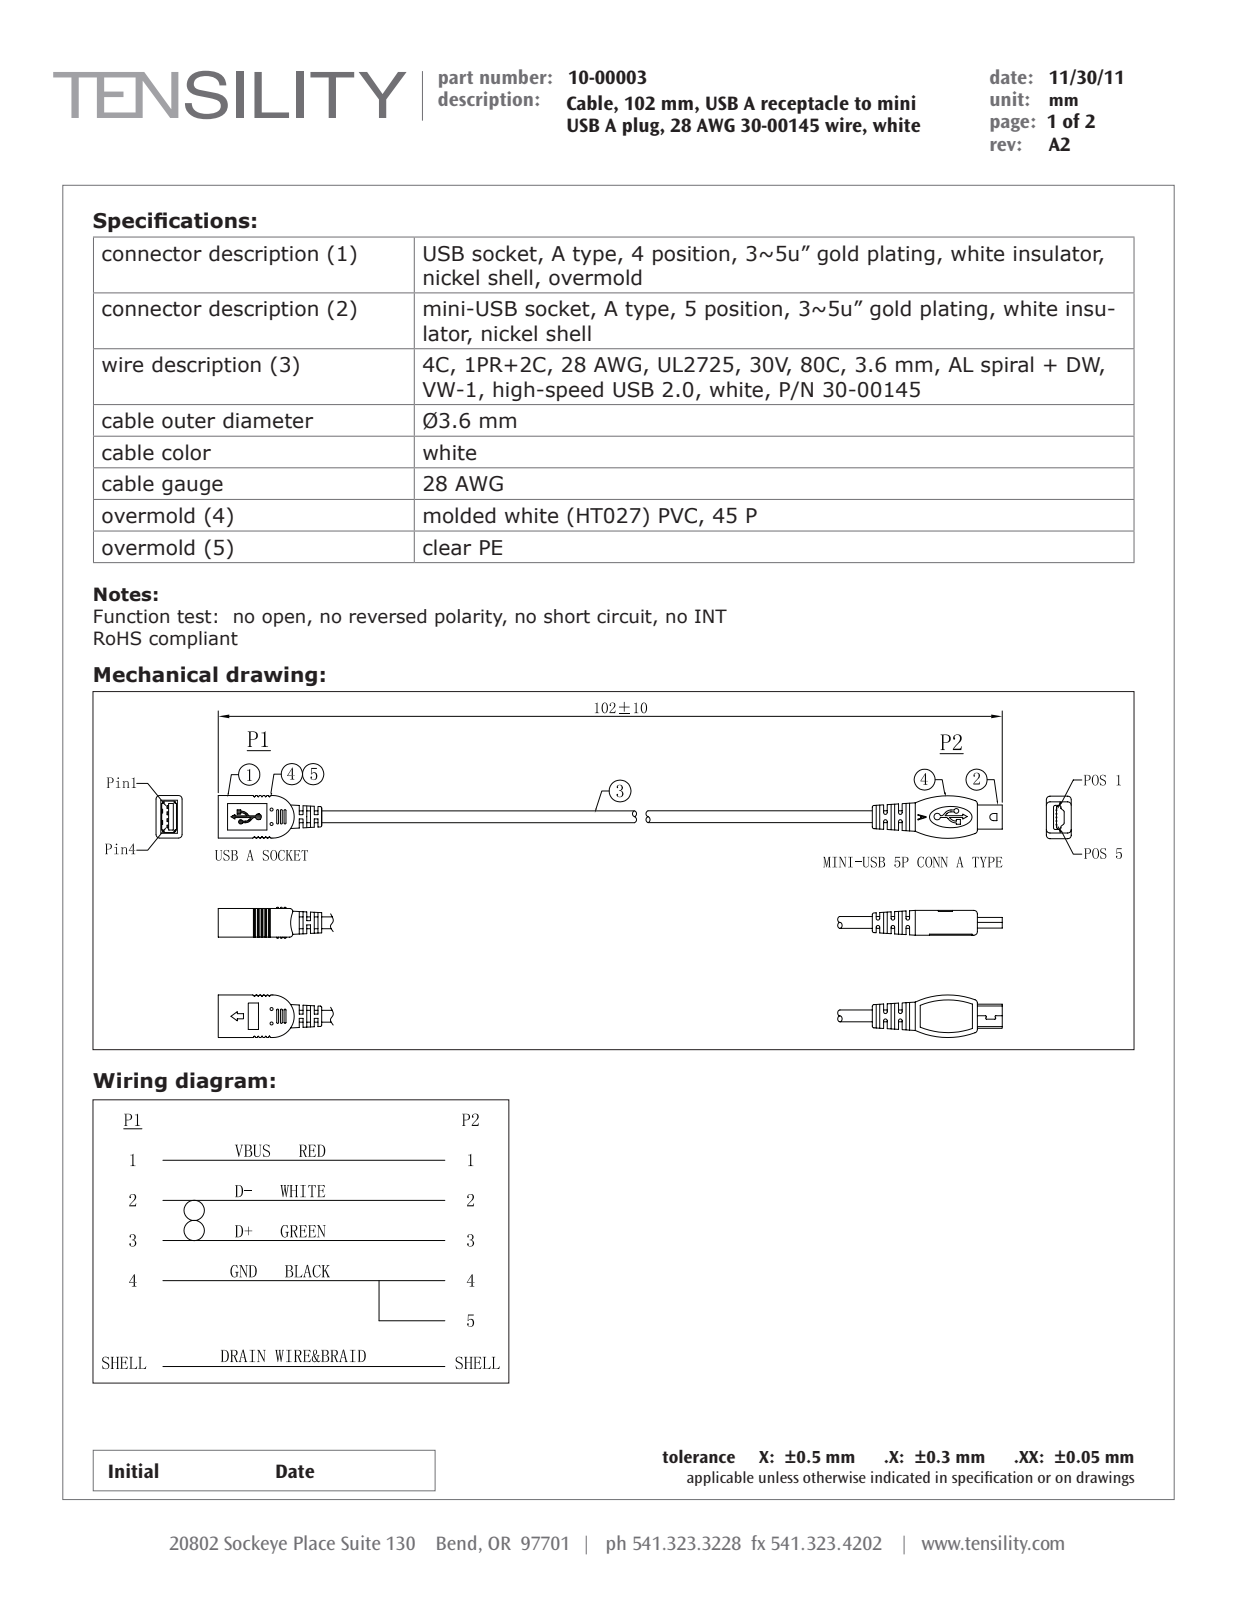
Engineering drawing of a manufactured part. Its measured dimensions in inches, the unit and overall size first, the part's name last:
Units: inches
Overall size (bounding box): 8.239 × 0.673 × 0.433
Round holes (diameter × count): ⌀0.099 ×1
Round bosses / shafts (diameter × count): ⌀0.033 ×4, ⌀0.187 ×1, ⌀0.142 ×1, ⌀0.138 ×1, ⌀0.118 ×1, ⌀0.096 ×1, ⌀0.057 ×1, ⌀0.051 ×1
Partial cylindrical surfaces — rounded edges, fillets, slot ends (radius × count): R0.008 ×44, R0.004 ×16, R0.02 ×14, R0.012 ×11, R0.01 ×8, R0.016 ×8, R0.079 ×6, R0.013 ×4
Main face-to-face distances: 0.051, 0.096, 0.298, 0.012, 0.136, 0.384, 0.074, 0.394, 0.288, 0.226
Hole centre spacings: 0.033, 0.029, 0.034, 0.036, 0.038, 0.031, 0.039, 0.041
Volume: 0.487 in³ · Surface area: 29.43 in²
Bodies: 107 solids, 1610 faces (641 planar, 529 cylindrical, 440 other)
Part name (STEP PRODUCT): 10-00003; 30-00099_blunt cut; 50-00424; 50-00424 shell (+6 more)
STEP written by: SolidWorks 2015 (CONFIG_CONTROL_DESIGN)
